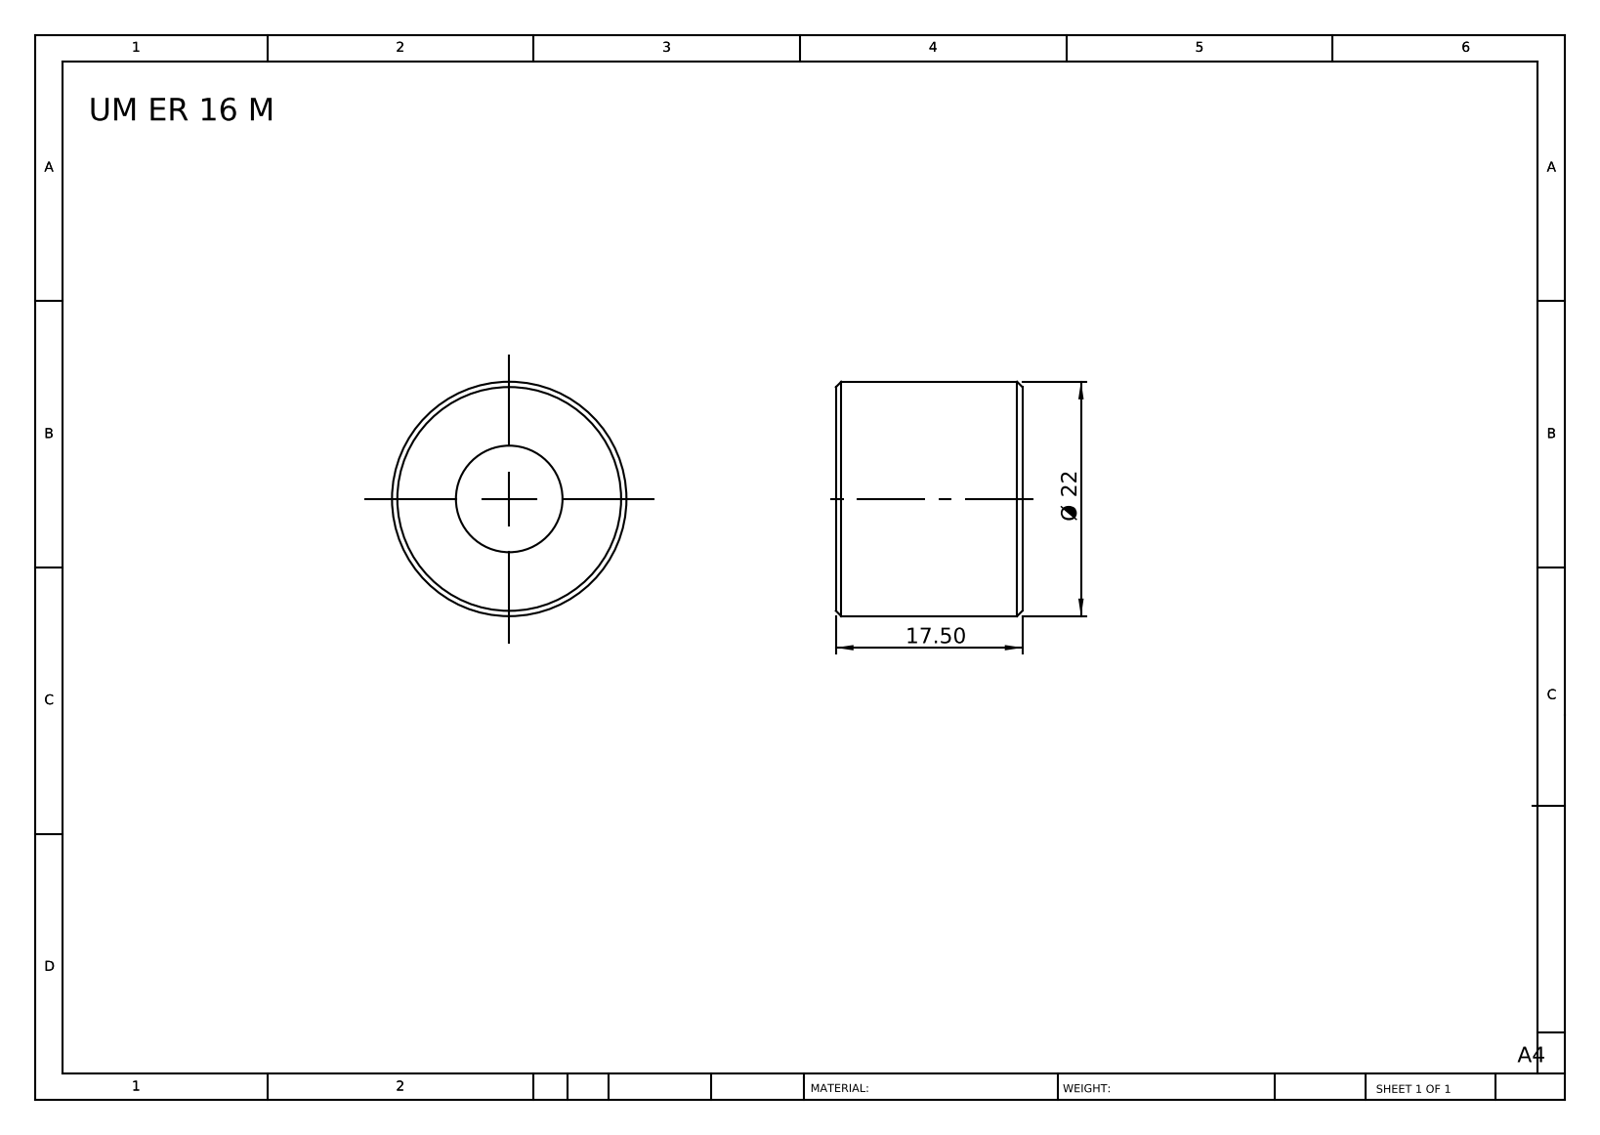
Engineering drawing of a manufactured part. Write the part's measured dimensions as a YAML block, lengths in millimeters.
part_name: "UM ER 16 M"
step_written_by: "SolidWorks 2014 (CONFIG_CONTROL_DESIGN)"
units: millimeters
bodies: {solids: 1, faces: 10, planar: 2, cylindrical: 4, other: 4}
overall_size: [22, 22, 17.5]
volume: 5261
surface_area: 2321
round_holes:
  - {diameter: 10, count: 1}
round_bosses_or_shafts:
  - {diameter: 22, count: 1}
face_to_face_distances: [17.5]
